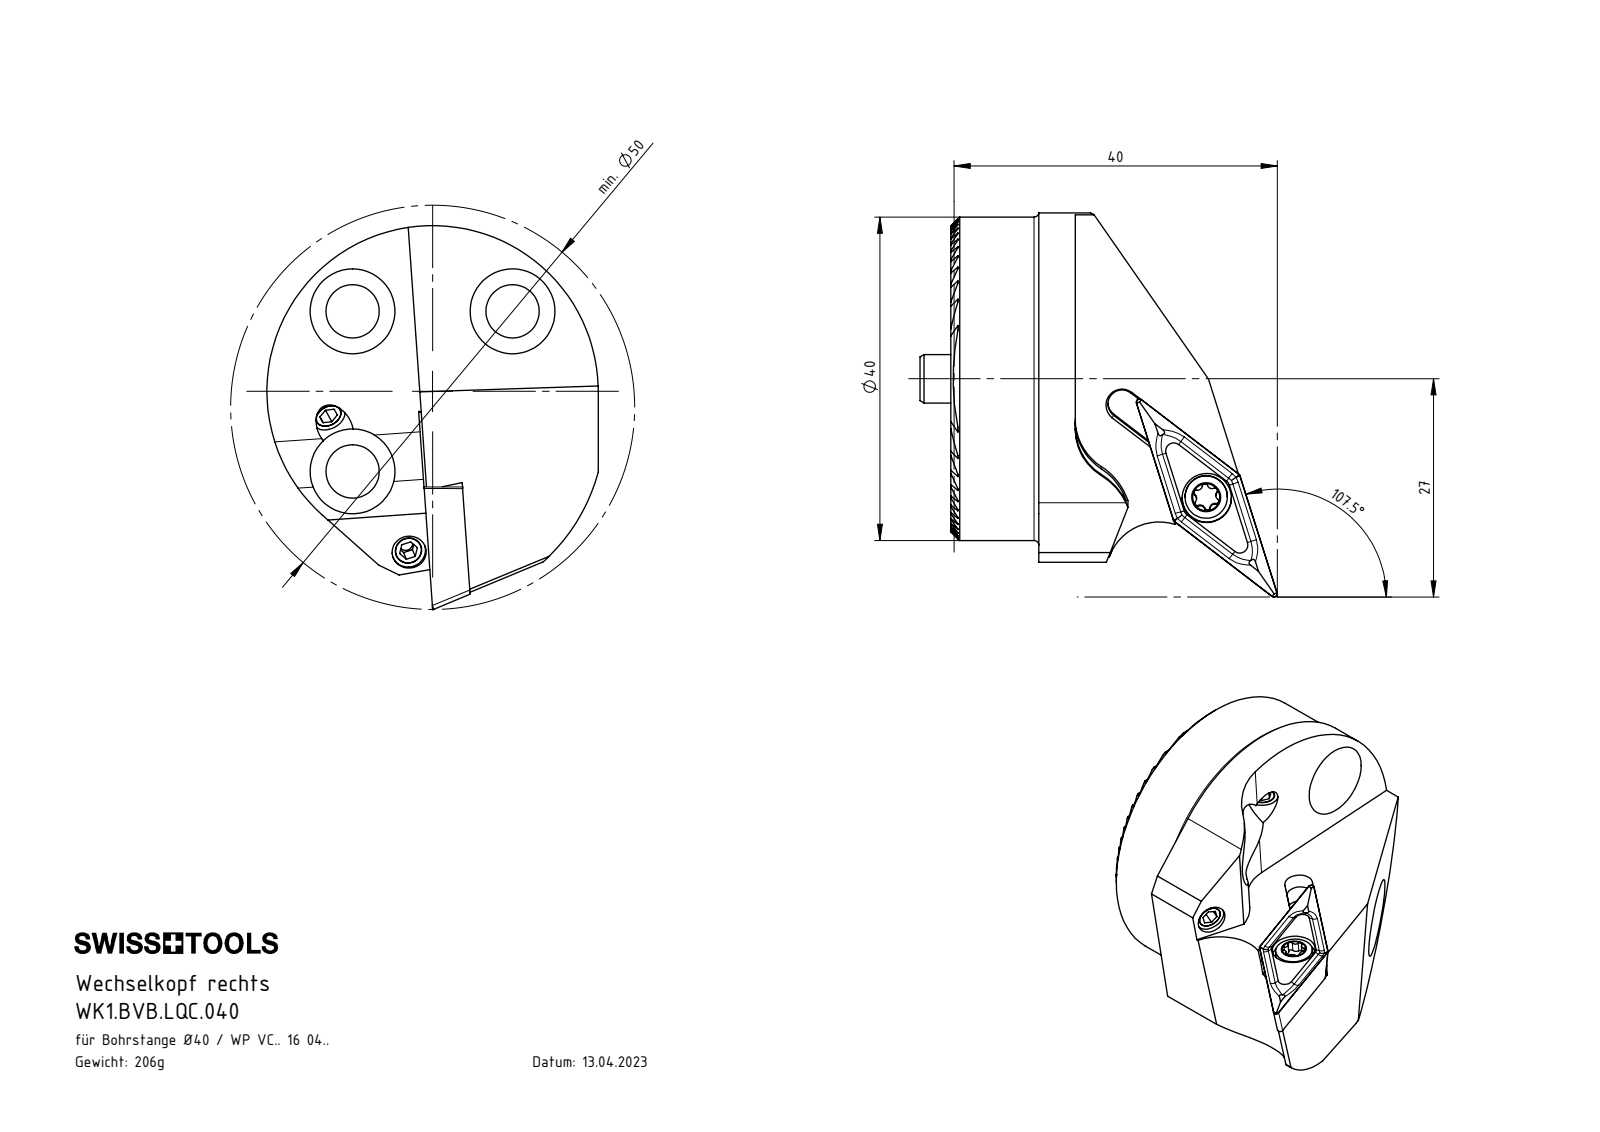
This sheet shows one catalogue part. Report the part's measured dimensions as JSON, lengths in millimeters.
{"part_name": "KVT_MB_600_040; WCB-ER2.001.009_A; WKX-ER1.004.005_A_PreviewCfg; WK1.BVB.LQC.040 (+3 more)", "step_written_by": "SolidWorks 2017 (AUTOMOTIVE_DESIGN)", "units": "millimeters", "bodies": {"solids": 10, "faces": 565, "planar": 218, "cylindrical": 197, "other": 150}, "overall_size": [47.5, 44.2, 41], "volume_mm3": 25806, "surface_area_mm2": 11340, "round_holes": [[3.3, 5], [4.2, 3], [6.6, 3], [10.5, 3], [1.7, 2], [3, 2], [4, 1], [4.4, 1], [6.1, 1], [12, 1]], "round_bosses_or_shafts": [[4, 5], [40, 1], [6, 1], [5.25, 1]], "partial_cylinders_radius": [[0.12, 26], [0.34, 6], [0.59, 6], [1.75, 1], [6.5, 1], [7, 1], [8, 1], [20.5, 1]], "face_to_face_distances": [1.3, 2.6, 3.9, 12.99, 5.2, 11.69, 9.09, 10.39, 7.79, 6.5], "hole_center_spacings": [14, 19.8, 28]}
